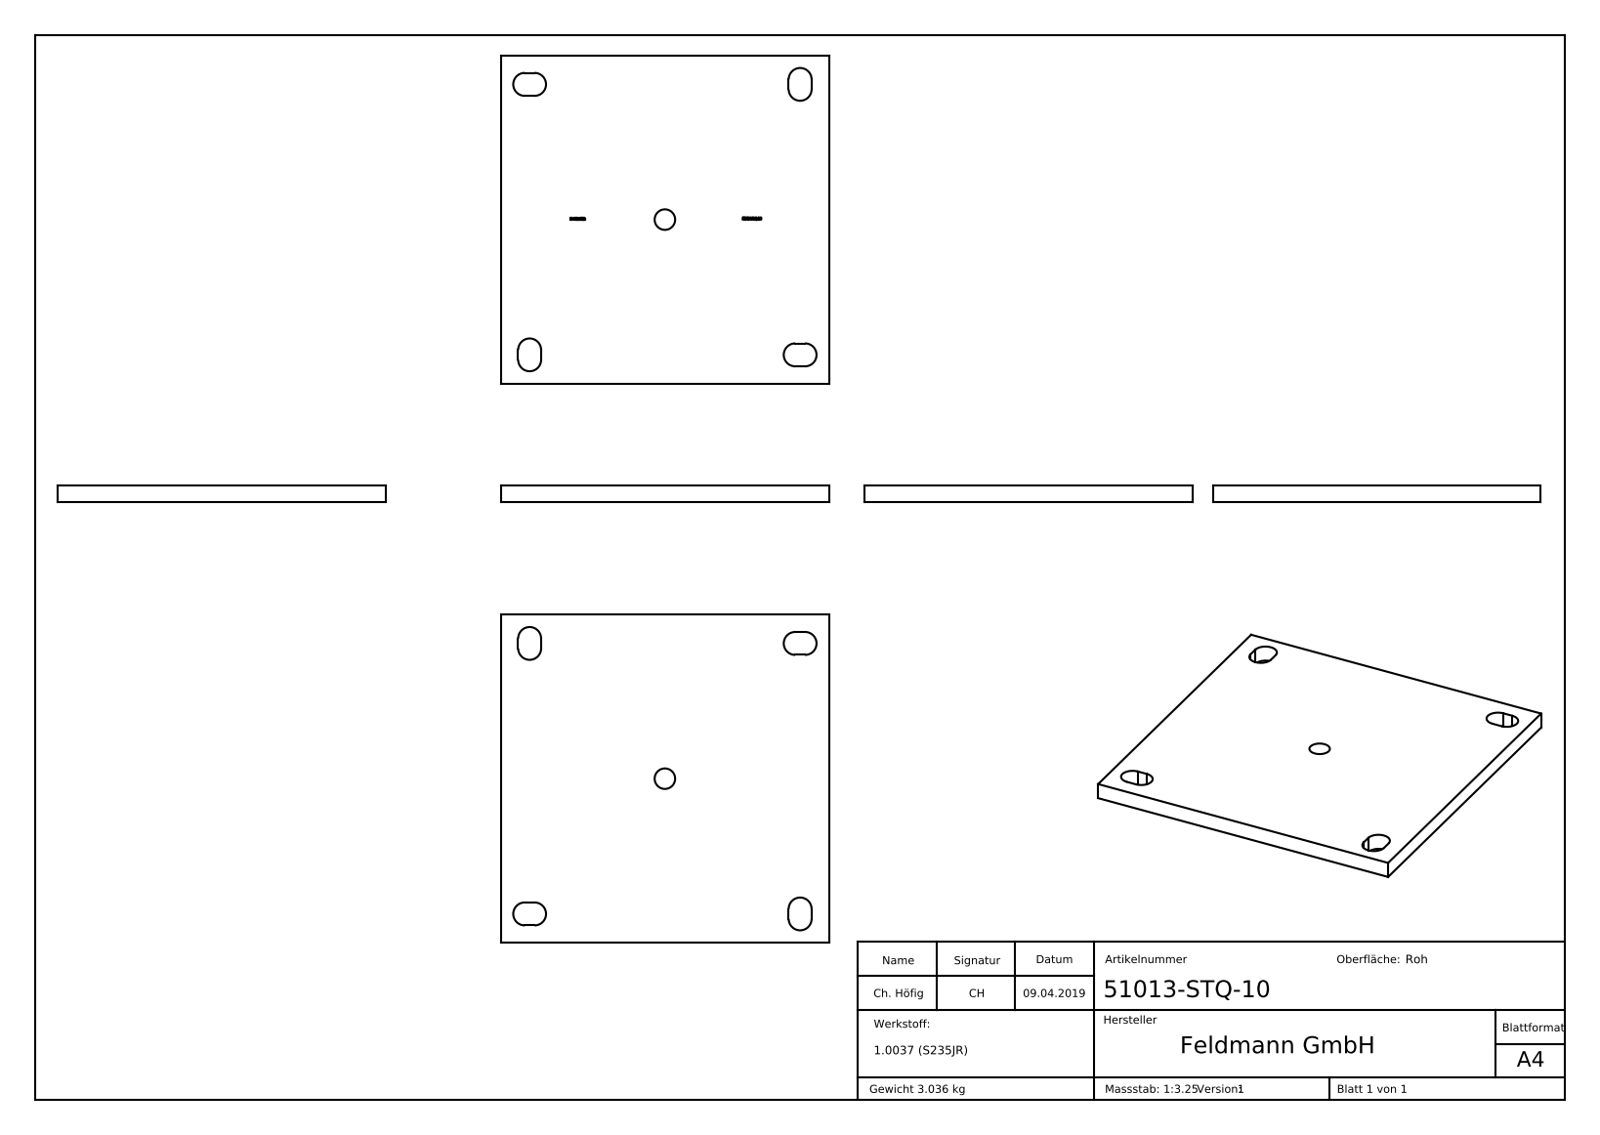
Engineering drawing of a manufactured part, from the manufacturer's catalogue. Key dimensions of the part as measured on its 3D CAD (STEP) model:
Part name (STEP PRODUCT): 51013-STQ-10
STEP written by: SolidWorks 2015 (CONFIG_CONTROL_DESIGN)
Units: millimetres
Bodies: 1 solid, 270 faces (145 planar, 12 cylindrical, 113 other)
Overall size (bounding box): 200 × 200 × 10
Volume: 389 255 mm³ · Surface area: 88 493 mm²
Round holes (diameter × count): ⌀12.5 ×1
Partial cylindrical surfaces — rounded edges, fillets, slot ends (radius × count): R7 ×8
Main face-to-face distances: 10, 200, 10.5, 24.5, 175.5, 189.5, 14, 165, 179, 151
